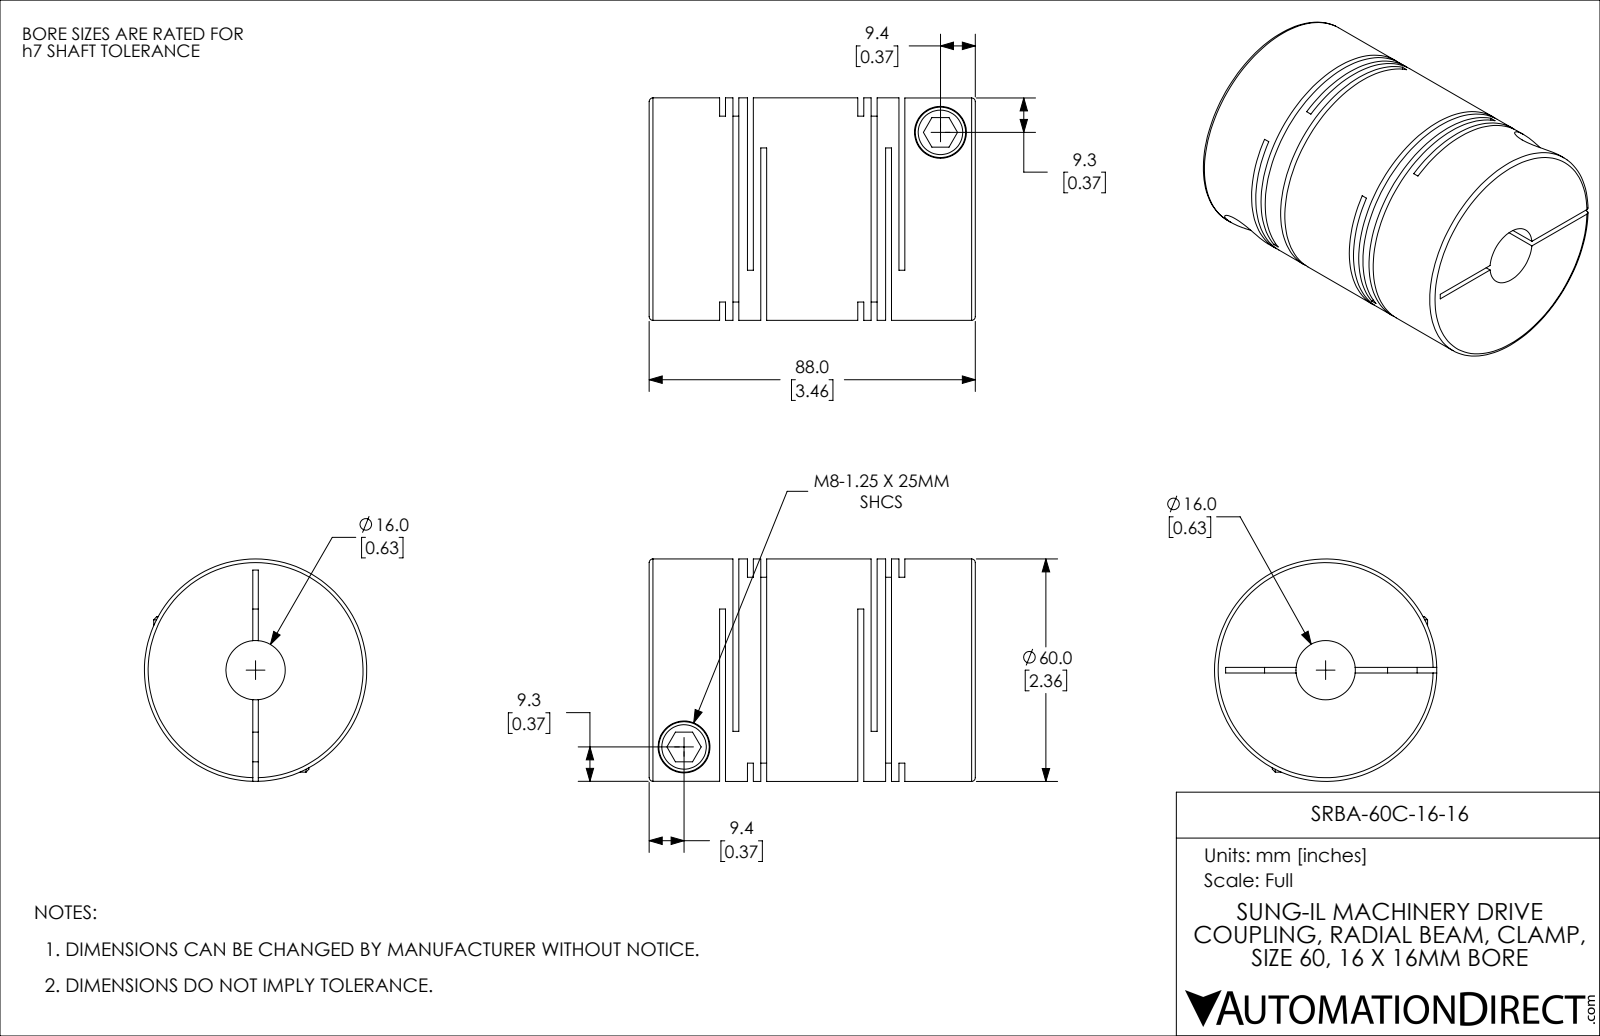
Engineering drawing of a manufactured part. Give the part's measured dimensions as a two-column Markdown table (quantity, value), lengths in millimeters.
| quantity | value |
| --- | --- |
| part name | SRBA-60C-16-16 |
| STEP written by | SolidWorks 2021 (CONFIG_CONTROL_DESIGN) |
| units | millimeters |
| bodies | 1 solid, 114 faces (60 planar, 42 cylindrical, 12 other) |
| overall size | 88 × 60 × 60 |
| volume | 198 322 mm³ |
| surface area | 63 469 mm² |
| round holes (diameter × count) | 8 × 2, 14 × 2, 16 × 1 |
| round bosses / shafts (diameter × count) | 13.6 × 2, 60 × 1 |
| main face-to-face distances | 1.6, 3.6, 7.5, 37.3, 2, 5.9, 3.9, 35.7, 33.7, 29.8 |
